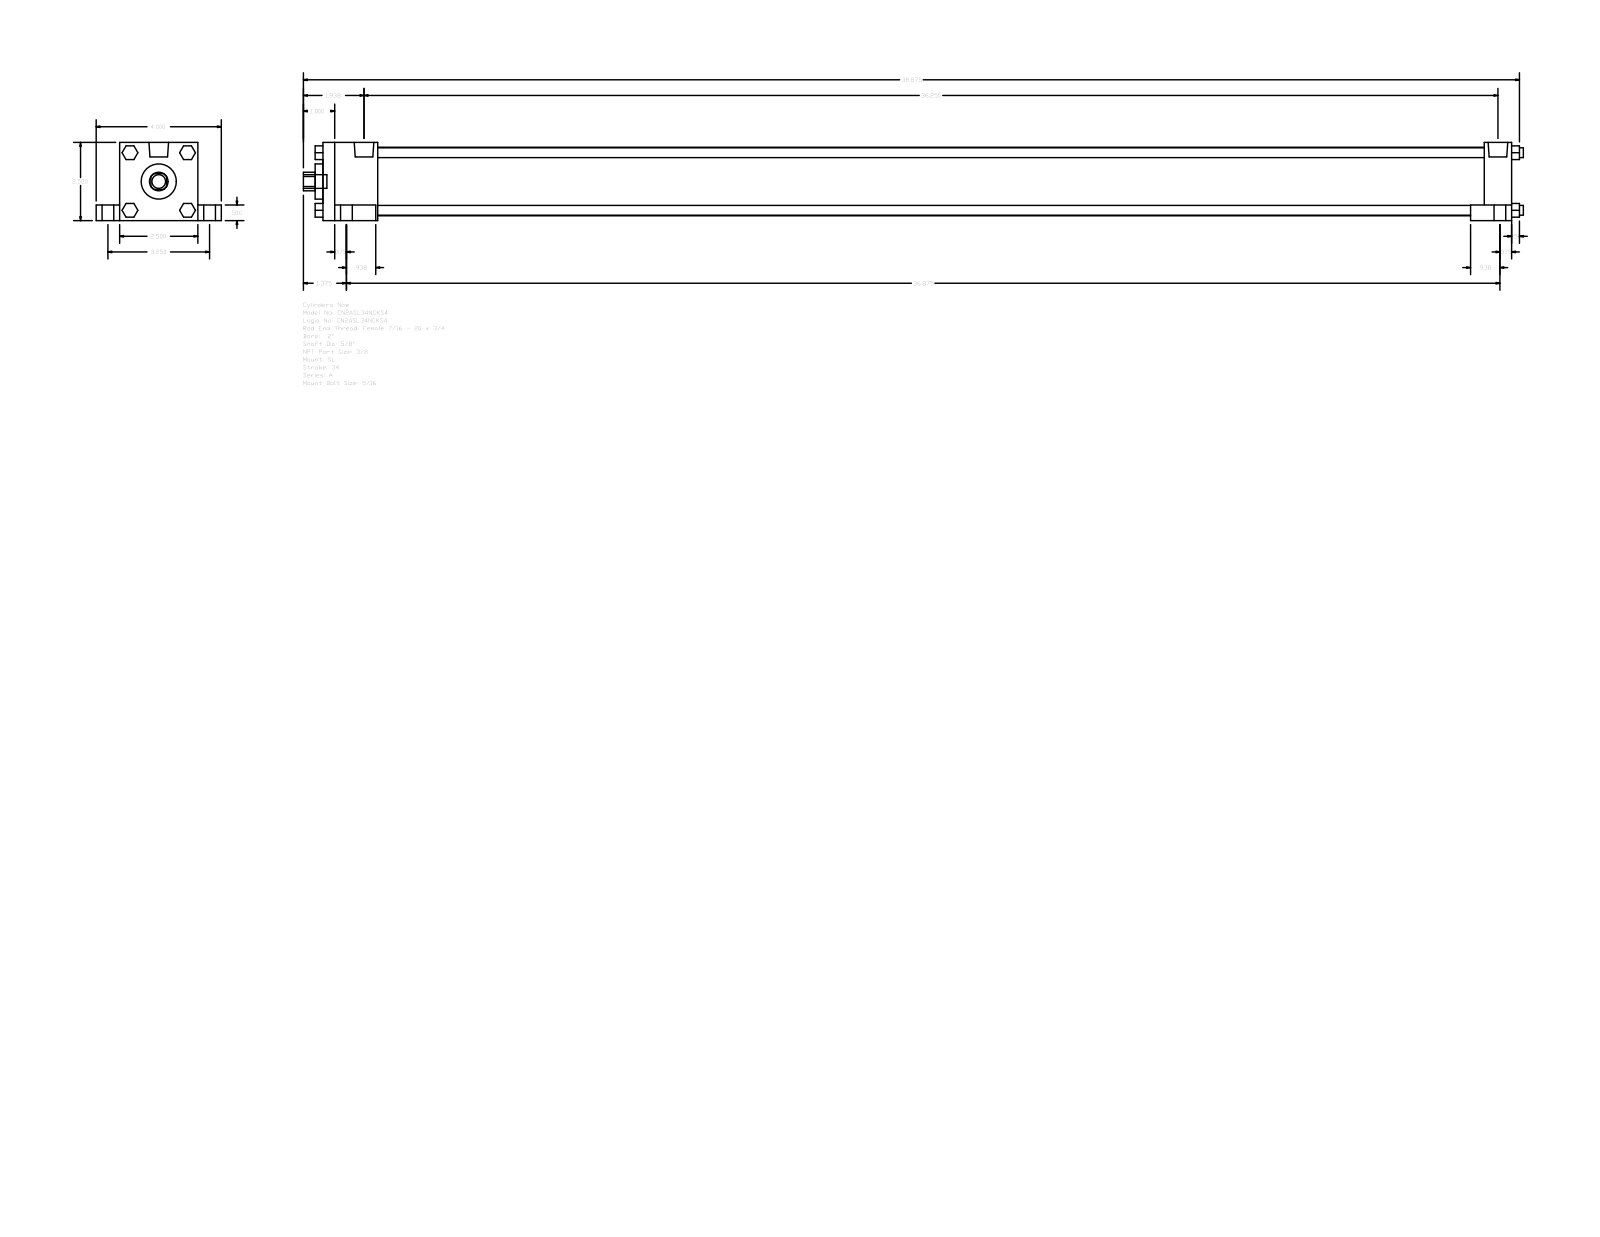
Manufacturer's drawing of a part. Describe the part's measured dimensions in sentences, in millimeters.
The part is named "A_SL__0200_0.625". Its 3-D file was written by "GSSL Pune (CONFIG_CONTROL_DESIGN)". It is 0 solids with 148 faces: 112 planar, 36 cylindrical and 0 other. Overall it measures 990.6 by 101.6 by 63.5 millimeters. Round holes: 1 of diameter 15.88, 1 of diameter 28.57, 1 of diameter 55.63. Round bosses or shafts: 4 of diameter 15.88, 4 of diameter 9.53, 4 of diameter 7.94, 4 of diameter 5.56, 2 of diameter 15.93, 1 of diameter 11.11. Partial cylindrical surfaces (rounded edges, fillets, slot ends): 1 of radius 7.54. The main face-to-face distances are 63.5, 965.2, 50.8, 12.7, 19.05, 82.55, 44.45, 920.75, 942.97, 898.52.
